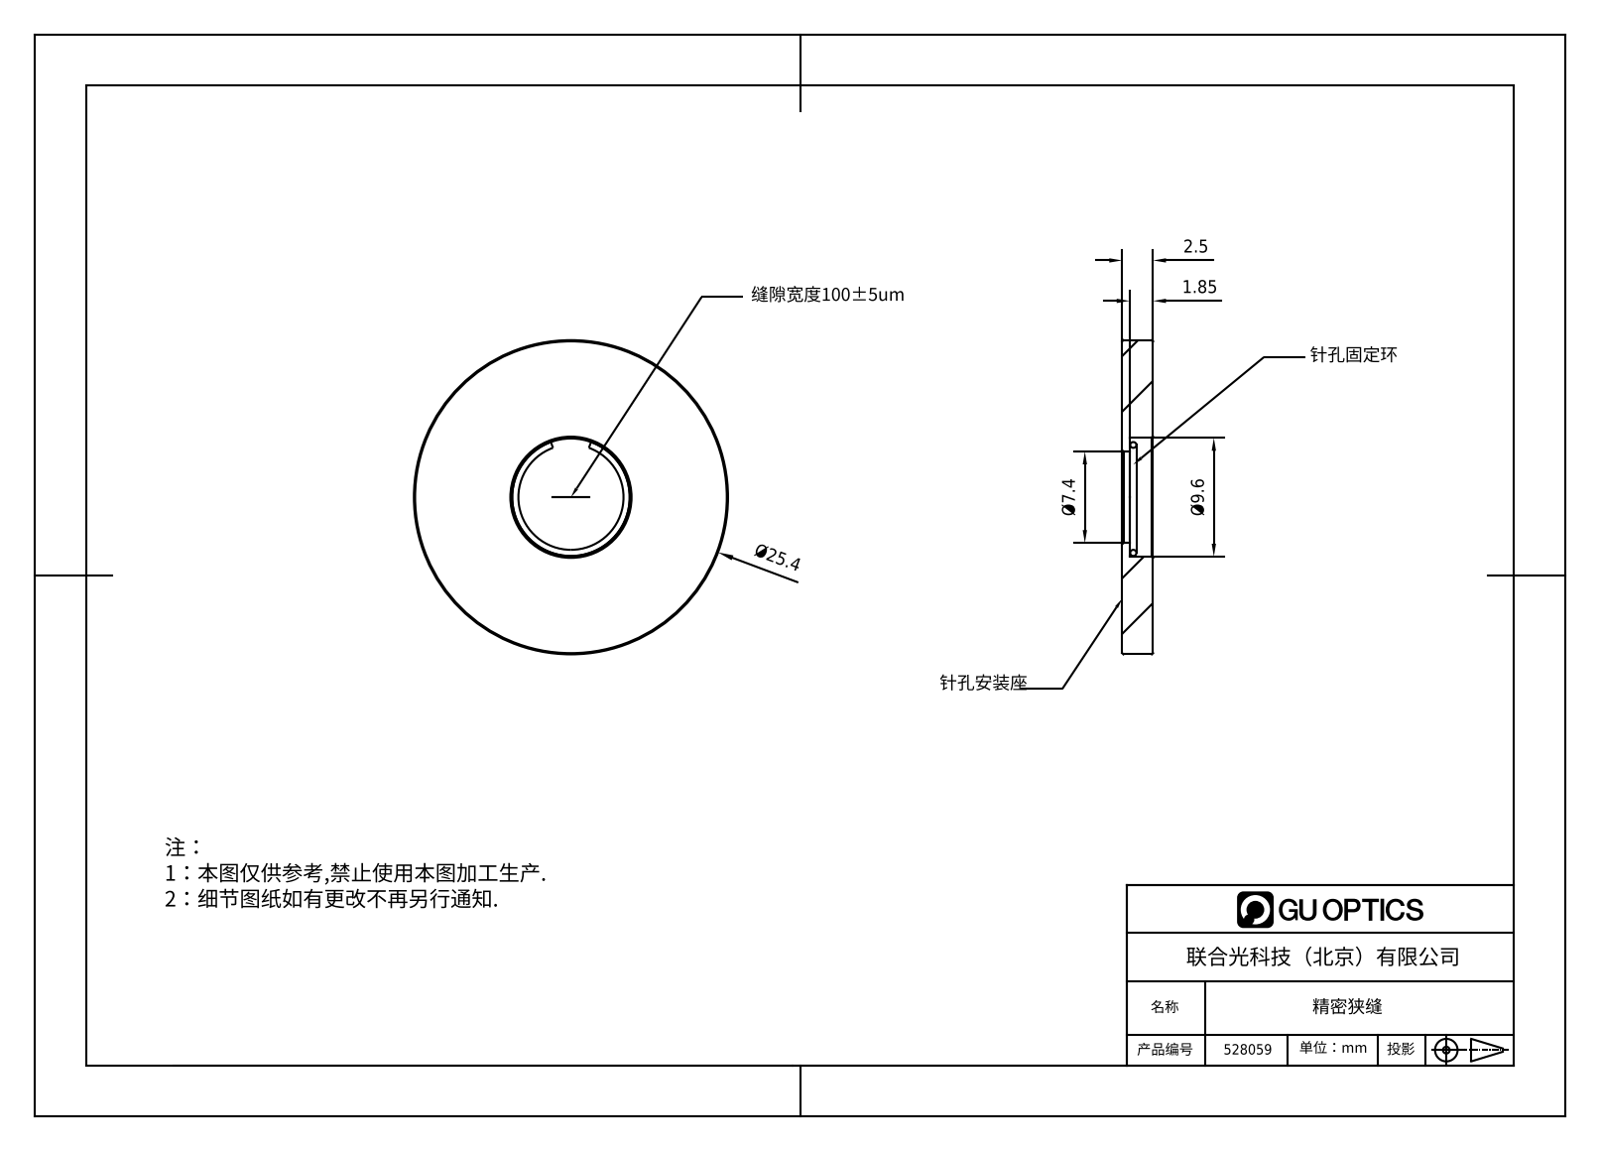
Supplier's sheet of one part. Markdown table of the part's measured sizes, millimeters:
| quantity | value |
| --- | --- |
| part name | 528059 |
| STEP written by | SolidWorks 2020 (CONFIG_CONTROL_DESIGN) |
| units | millimeters |
| bodies | 2 solids, 33 faces (11 planar, 8 cylindrical, 14 other) |
| overall size | 25.4 × 25.4 × 2.5 |
| volume | 1 111 mm³ |
| surface area | 1 313 mm² |
| round holes (diameter × count) | 7.4 × 1, 9.6 × 1 |
| round bosses / shafts (diameter × count) | 25.4 × 1, 9.5 × 1 |
| main face-to-face distances | 2.5, 0.65, 1.85, 0.6, 1.9, 3 |
